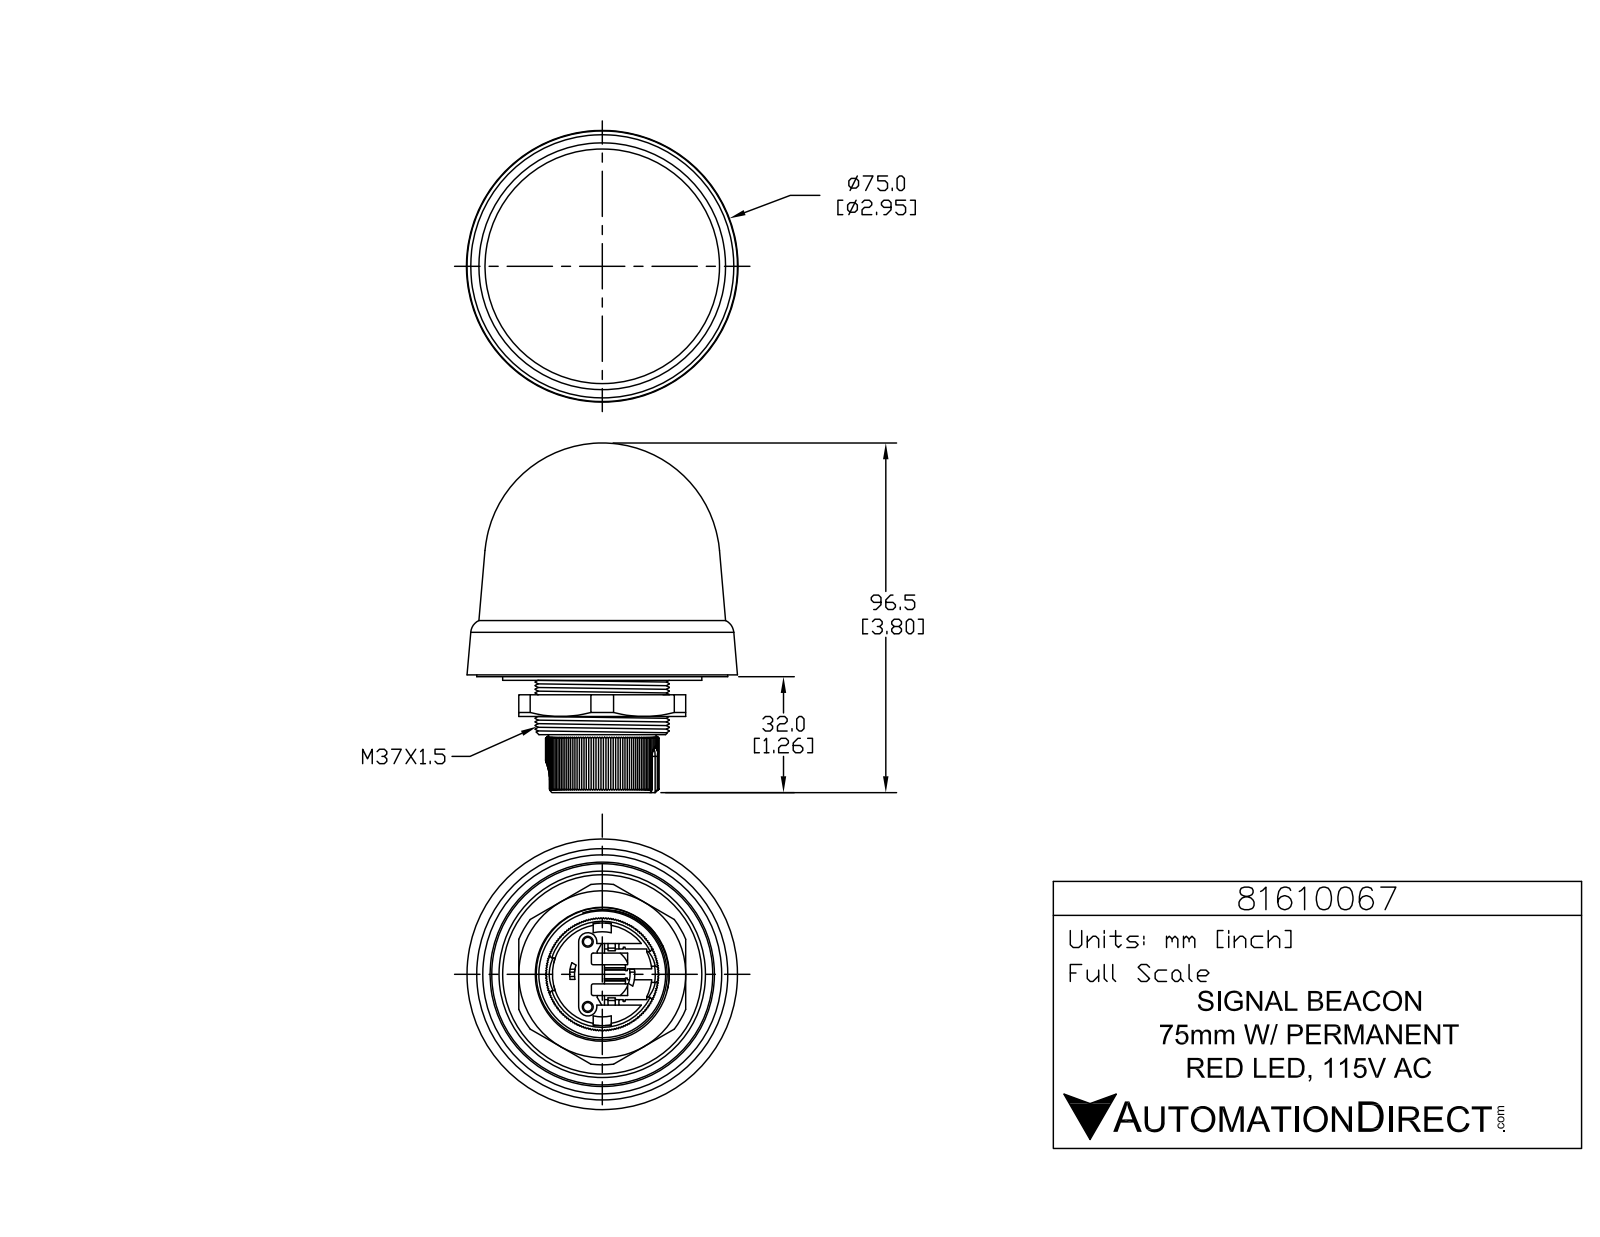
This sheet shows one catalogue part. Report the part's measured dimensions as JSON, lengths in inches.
{"part_name": "81610067", "step_written_by": "SolidWorks 2019 (CONFIG_CONTROL_DESIGN)", "units": "inches", "bodies": {"solids": 3, "faces": 560, "planar": 432, "cylindrical": 80, "other": 48}, "overall_size": [3.799, 2.941, 2.941], "volume_in3": 12.36, "surface_area_in2": 58.68, "round_holes": [[0.094, 2], [0.118, 2], [0.604, 1], [1.142, 1]], "round_bosses_or_shafts": [[0.217, 2], [0.067, 2], [2.165, 1], [1.457, 1], [0.925, 1]], "partial_cylinders_radius": [[0.008, 6], [0.039, 6], [0.02, 4], [0.031, 2], [0.079, 2], [0.098, 2], [0.177, 1], [0.354, 1]], "face_to_face_distances": [0.177, 0.354, 0.197, 0.433, 0.512, 0.335, 0.059, 0.394, 0.118, 0.157], "hole_center_spacings": [0.388, 0.709]}
